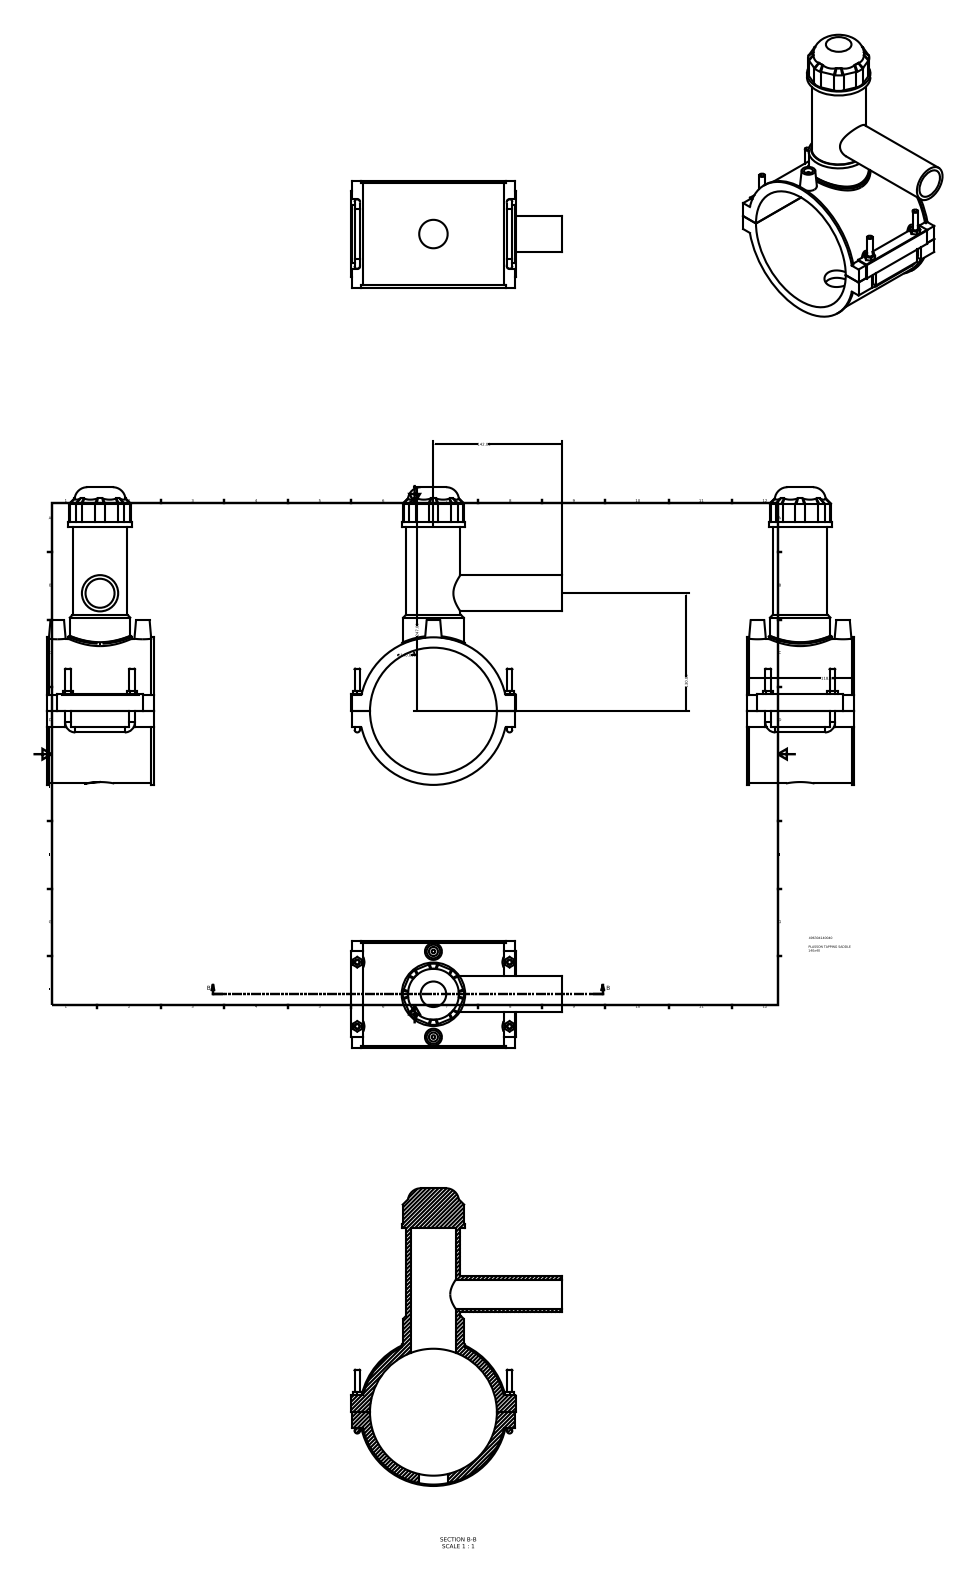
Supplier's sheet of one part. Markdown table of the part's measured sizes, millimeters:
| quantity | value |
| --- | --- |
| part name | 496304140040 |
| STEP written by | Autodesk Inventor 2015 (AUTOMOTIVE_DESIGN) |
| units | millimeters |
| bodies | 1 solid, 207 faces (118 planar, 48 cylindrical, 41 other) |
| overall size | 328.4 × 233 × 118 |
| volume | 942 912 mm³ |
| surface area | 228 030 mm² |
| round holes (diameter × count) | 10 × 2, 31.36 × 1, 32 × 1, 49 × 1, 140 × 1 |
| round bosses / shafts (diameter × count) | 6 × 6, 4 × 2, 162.79 × 1, 159.6 × 1, 70 × 1, 66.5 × 1, 59.5 × 1, 40 × 1 |
| partial cylindrical surfaces (radius × count) | 14 × 8, 3 × 4, 7.5 × 4, 0.5 × 1, 82.99 × 1 |
| main face-to-face distances | 118, 1, 181, 17.45, 17.55, 202.8, 202.7, 220.25, 180, 36 |
| hole center spacings | 47.2, 94.4 |
